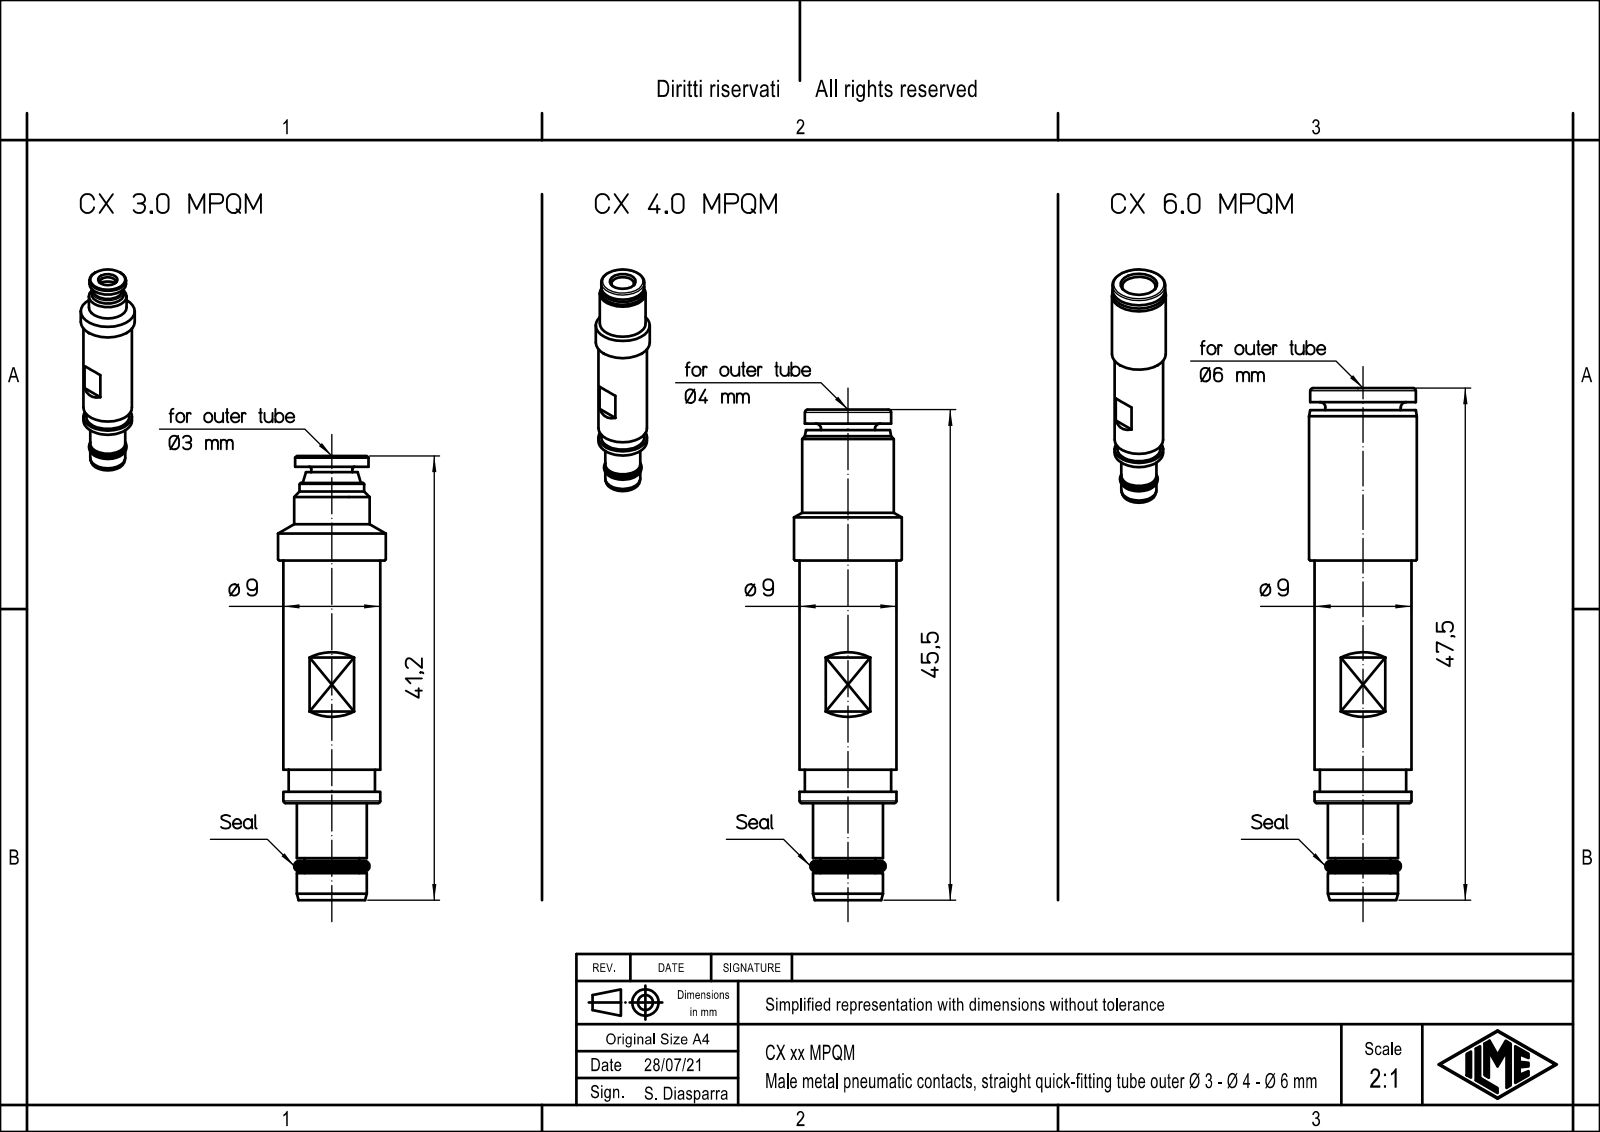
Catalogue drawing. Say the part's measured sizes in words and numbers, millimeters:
The part is named "CX_3.0_MPQM". Its 3-D file was written by "Creo Elements/Direct Modeling 20.1B 02-Apr-2019 (C) Parametric Technology GmbH (AUTOMOTIVE_DESIGN)". It is 1 solid with 77 faces: 25 planar, 28 cylindrical and 24 other. Overall it measures 41.2 by 10 by 10 millimeters. Its volume is 1 708 cubic millimeters and its surface area 1 752 square millimeters. Round holes: 1 of diameter 3, 1 of diameter 3.8. Round bosses or shafts: 1 of diameter 10, 1 of diameter 9, 1 of diameter 8, 1 of diameter 7, 1 of diameter 6.8, 1 of diameter 6.5, 1 of diameter 6, 1 of diameter 5.1. The main face-to-face distances are 2.5, 1, 32.2, 31.2, 8, 8.2, 27.6, 9, 40.2, 41.2.
